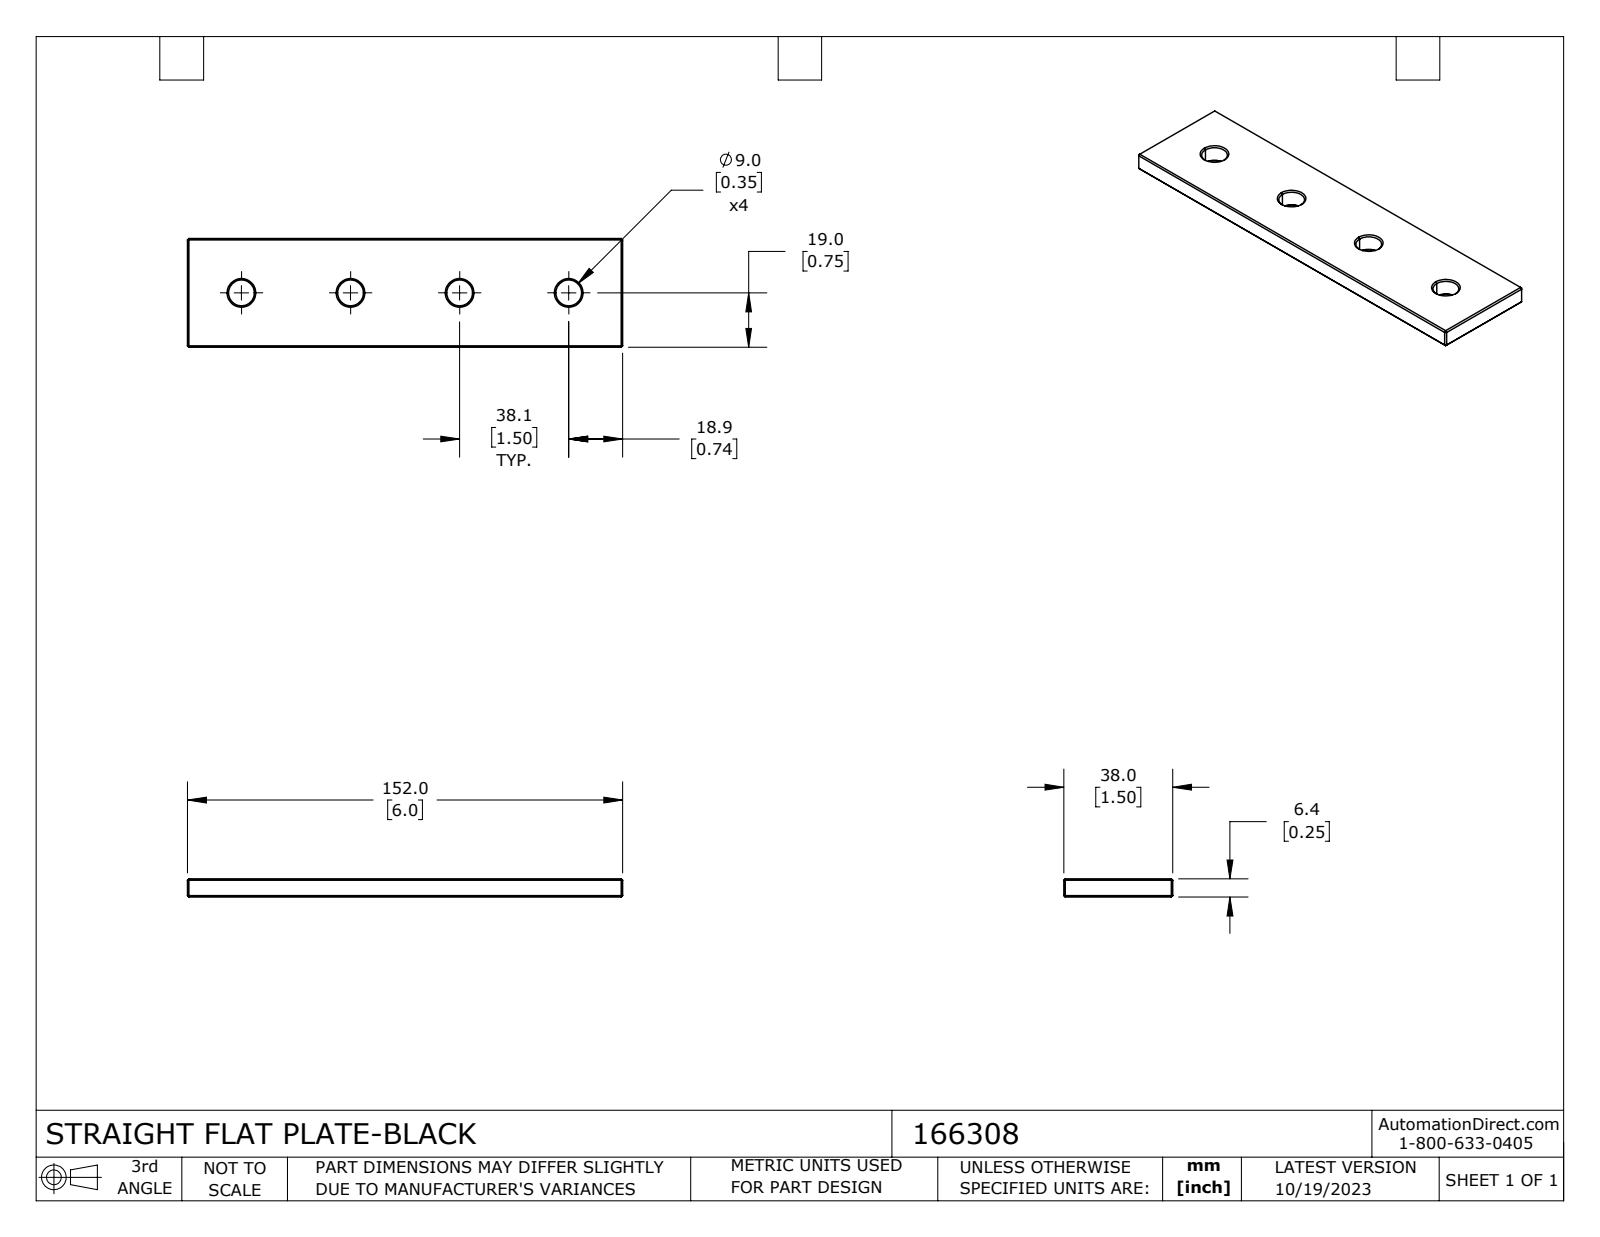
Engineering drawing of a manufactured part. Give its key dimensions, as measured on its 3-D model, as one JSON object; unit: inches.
{"part_name": "166308", "step_written_by": "SolidWorks 2023 (CONFIG_CONTROL_DESIGN)", "units": "inches", "bodies": {"solids": 1, "faces": 50, "planar": 26, "cylindrical": 8, "other": 16}, "overall_size": [5.984, 1.496, 0.25], "volume_in3": 2.132, "surface_area_in2": 21.51, "round_holes": [[0.354, 4]], "face_to_face_distances": [0.25, 1.496, 1.207, 5.984, 4.38, 5.261, 4.415], "hole_center_spacings": [1.5, 3, 4.5]}
